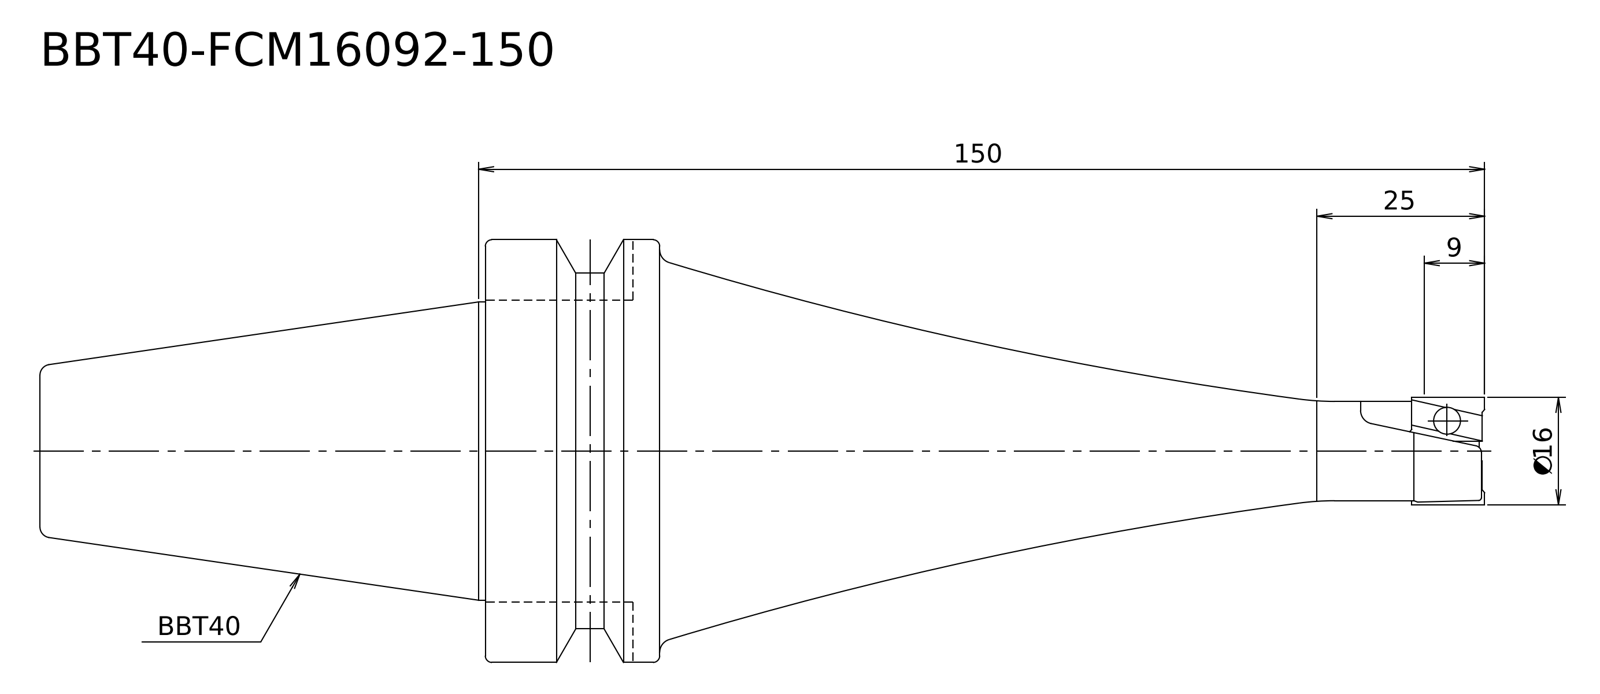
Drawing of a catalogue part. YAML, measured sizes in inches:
step_written_by: "Kubotek KeyCreator V8.5.1 (14335) (CONFIG_CONTROL_DESIGN)"
units: inches
bodies: {solids: 1, faces: 17, planar: 4, cylindrical: 6, other: 7}
overall_size: [8.48, 2.48, 2.48]
volume: 15.5
surface_area: 44.2
round_bosses_or_shafts:
  - {diameter: 2.48, count: 1}
  - {diameter: 2.087, count: 1}
  - {diameter: 1.75, count: 1}
  - {diameter: 0.63, count: 1}
  - {diameter: 0.583, count: 1}
face_to_face_distances: [2.614, 1.024, 3.638, 4.843, 5.866, 8.48]
